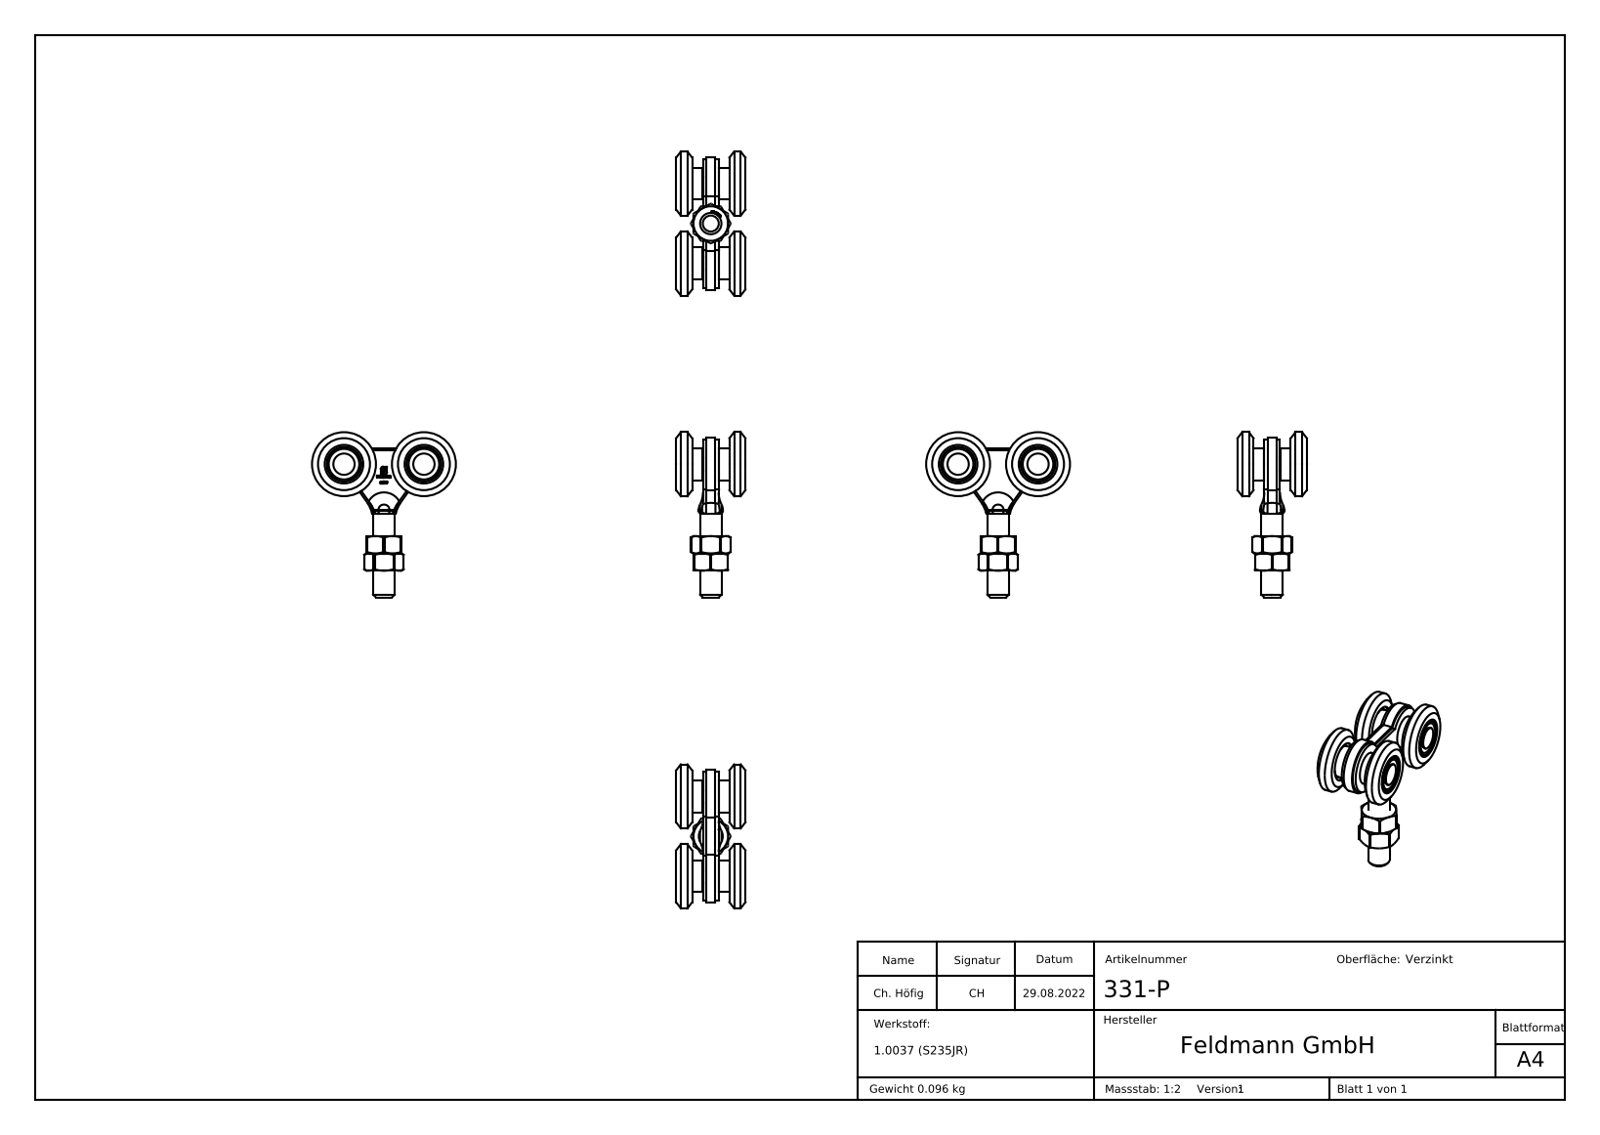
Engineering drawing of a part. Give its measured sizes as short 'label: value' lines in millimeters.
name: 331-P; 331-X-X Teil1_331-P Teil1; DIN 934 M4-M20_DIN 934 M8
written by: SolidWorks 2018 (CONFIG_CONTROL_DESIGN)
unit: mm
bodies: 17 solids, 914 faces (470 planar, 79 cylindrical, 365 other)
size: 62 × 54 × 26
volume: 19 087 mm³; area: 13 519 mm²
holes: 2× ⌀5, 2× ⌀12.3, 2× ⌀14.5, 1× ⌀6.8
bosses: 3× ⌀8, 2× ⌀24, 2× ⌀13, 2× ⌀12, 2× ⌀4.8
rounds: 12× R0.5, 6× R10, 2× R9.3, 1× R4.5
face distances: 20, 4.7, 10.05, 1.3, 10, 15.95, 5.9, 6, 9.95, 11.25
hole spacings: 30
